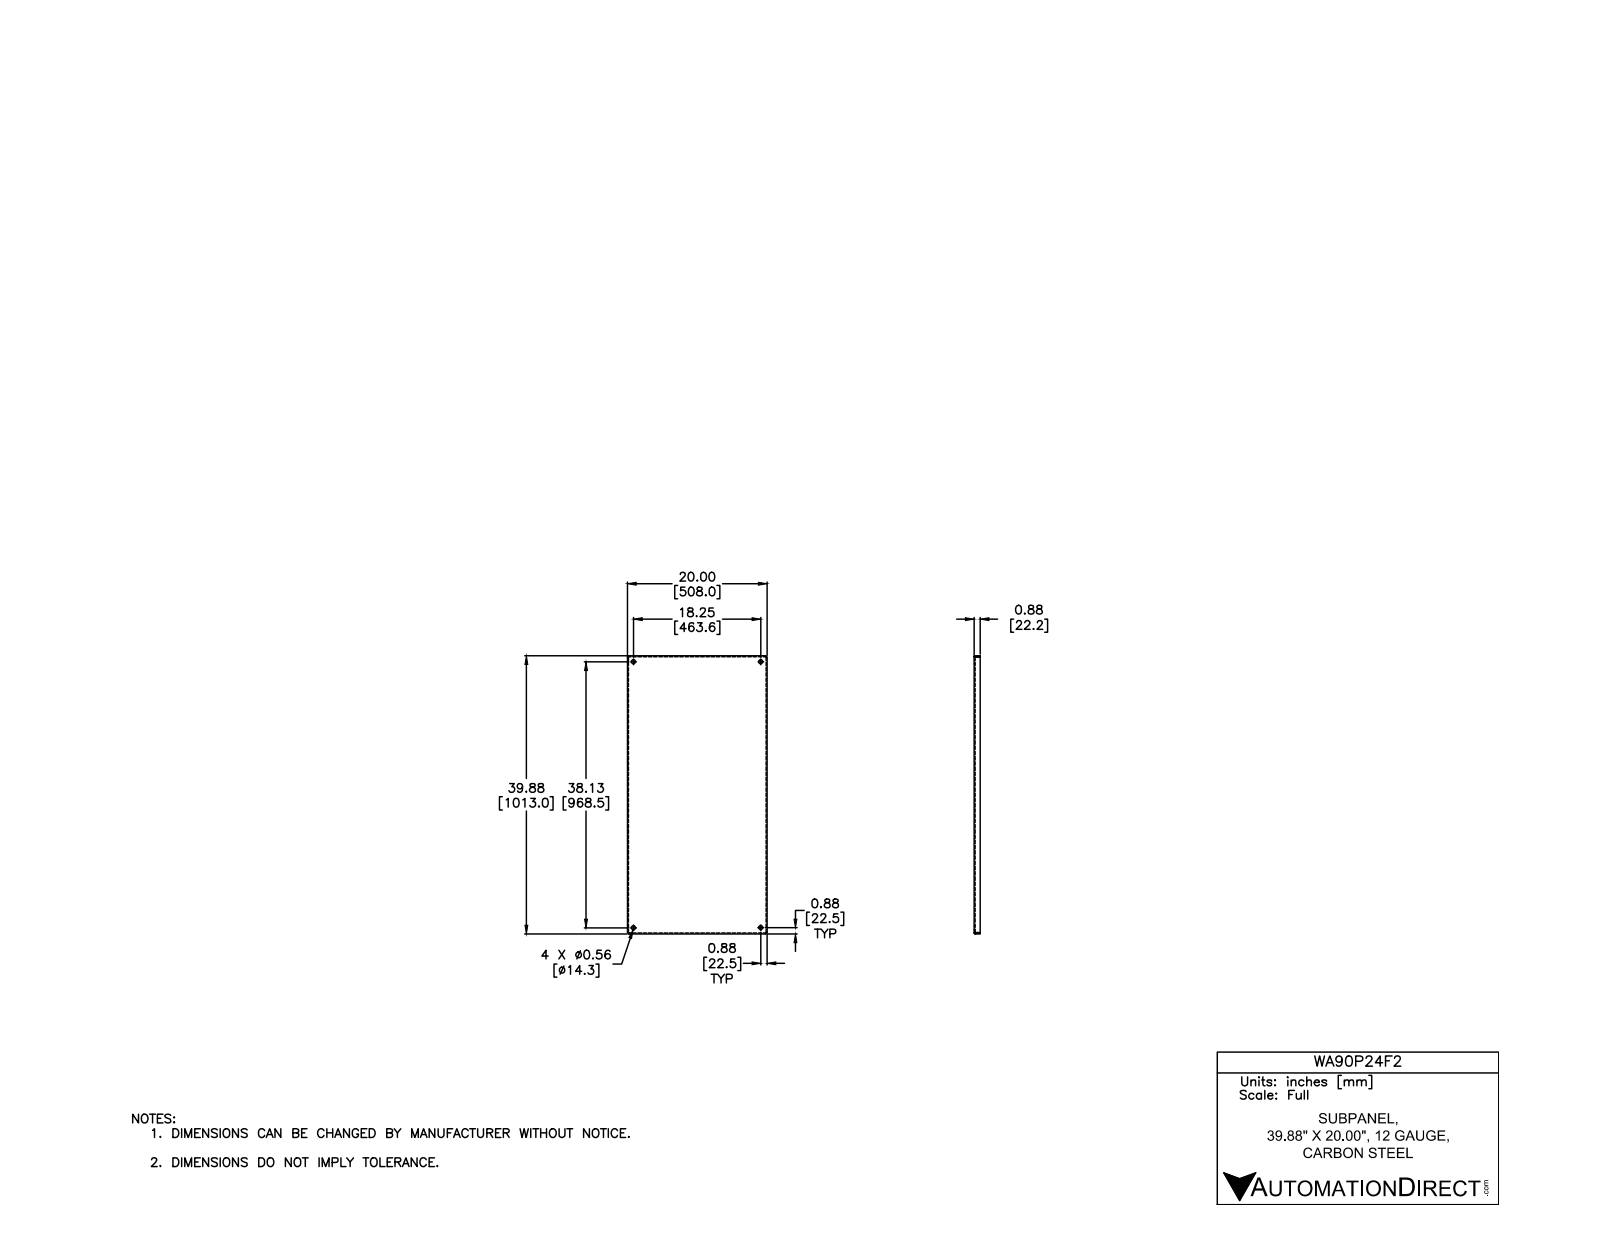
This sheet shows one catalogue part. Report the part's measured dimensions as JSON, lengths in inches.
{"part_name": "WA_P_F", "step_written_by": "Autodesk Inventor 2012 (AUTOMOTIVE_DESIGN)", "units": "inches", "bodies": {"solids": 1, "faces": 42, "planar": 22, "cylindrical": 12, "other": 8}, "overall_size": [39.88, 20, 0.875], "volume_in3": 82.98, "surface_area_in2": 1783, "round_holes": [[0.563, 4]], "partial_cylinders_radius": [[0.031, 4], [0.125, 4]], "face_to_face_distances": [0.094, 19.906, 20, 19.813, 39.786, 39.88, 39.693, 0.781, 0.875, 0.16], "hole_center_spacings": [18.25, 38.13, 42.272]}
